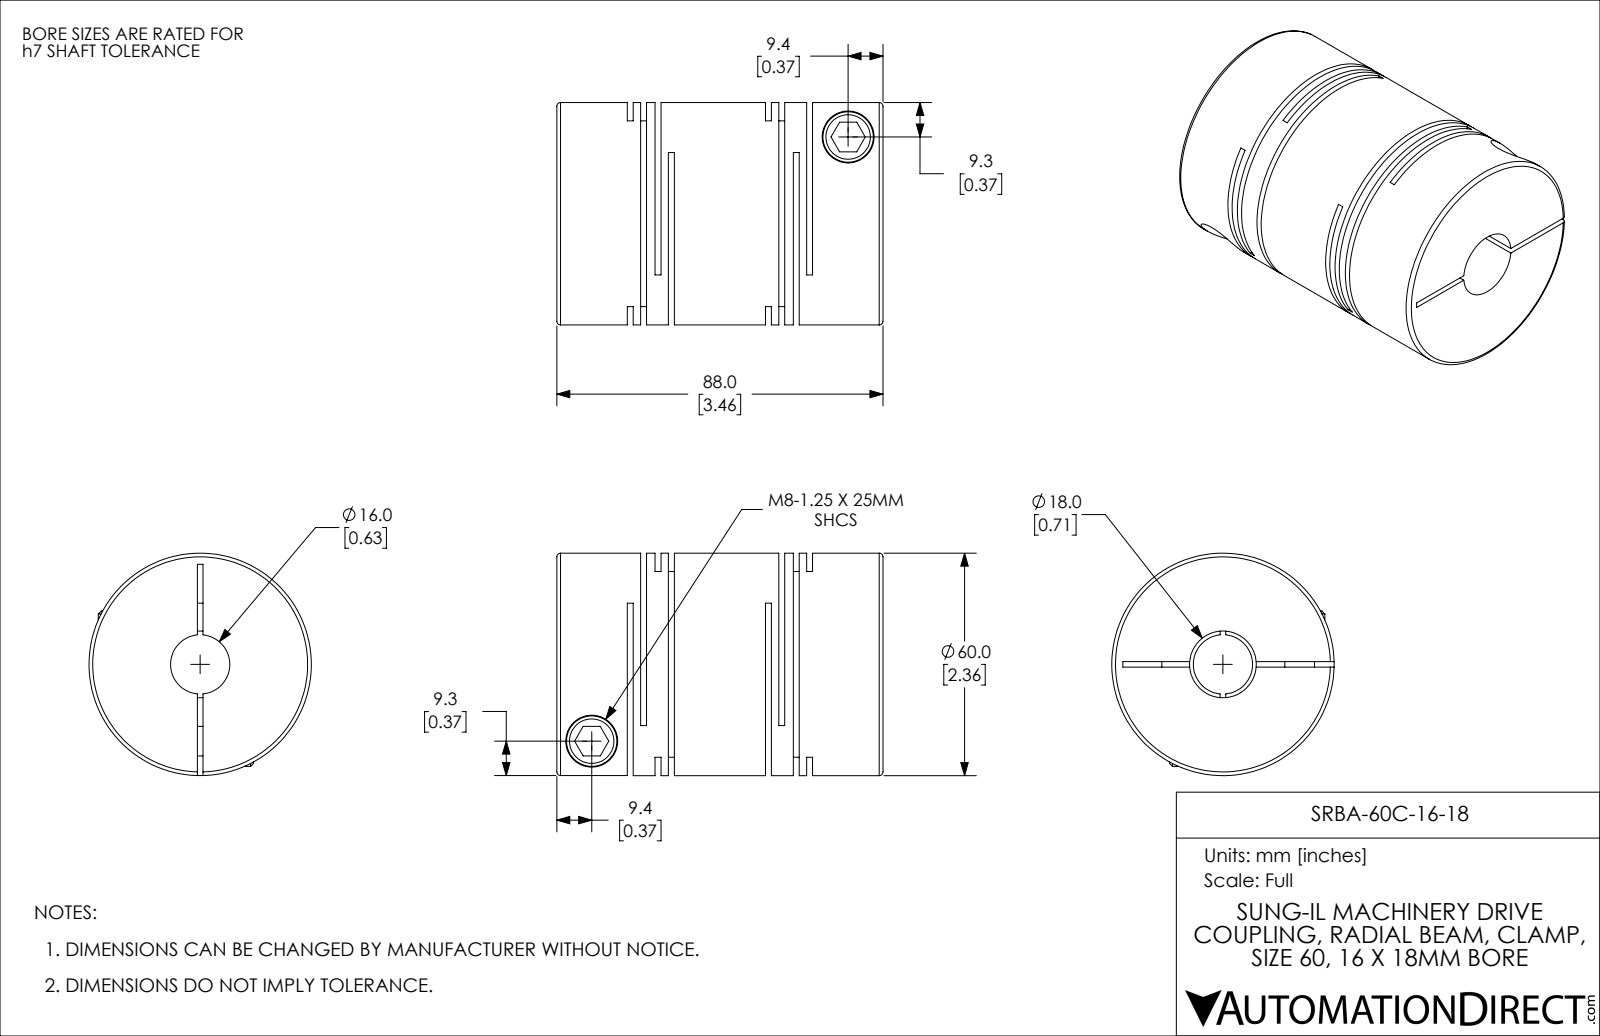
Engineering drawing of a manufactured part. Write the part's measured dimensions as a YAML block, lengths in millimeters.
part_name: "SRBA-60C-16-18"
step_written_by: "SolidWorks 2021 (CONFIG_CONTROL_DESIGN)"
units: millimeters
bodies: {solids: 1, faces: 114, planar: 60, cylindrical: 42, other: 12}
overall_size: [88, 60, 60]
volume: 195377
surface_area: 62897
round_holes:
  - {diameter: 8, count: 2}
  - {diameter: 14, count: 2}
  - {diameter: 16, count: 1}
  - {diameter: 18, count: 1}
round_bosses_or_shafts:
  - {diameter: 13.6, count: 2}
  - {diameter: 60, count: 1}
face_to_face_distances: [1.6, 7.5, 37.3, 3.6, 2, 5.9, 35.7, 3.9, 33.7, 29.8]
